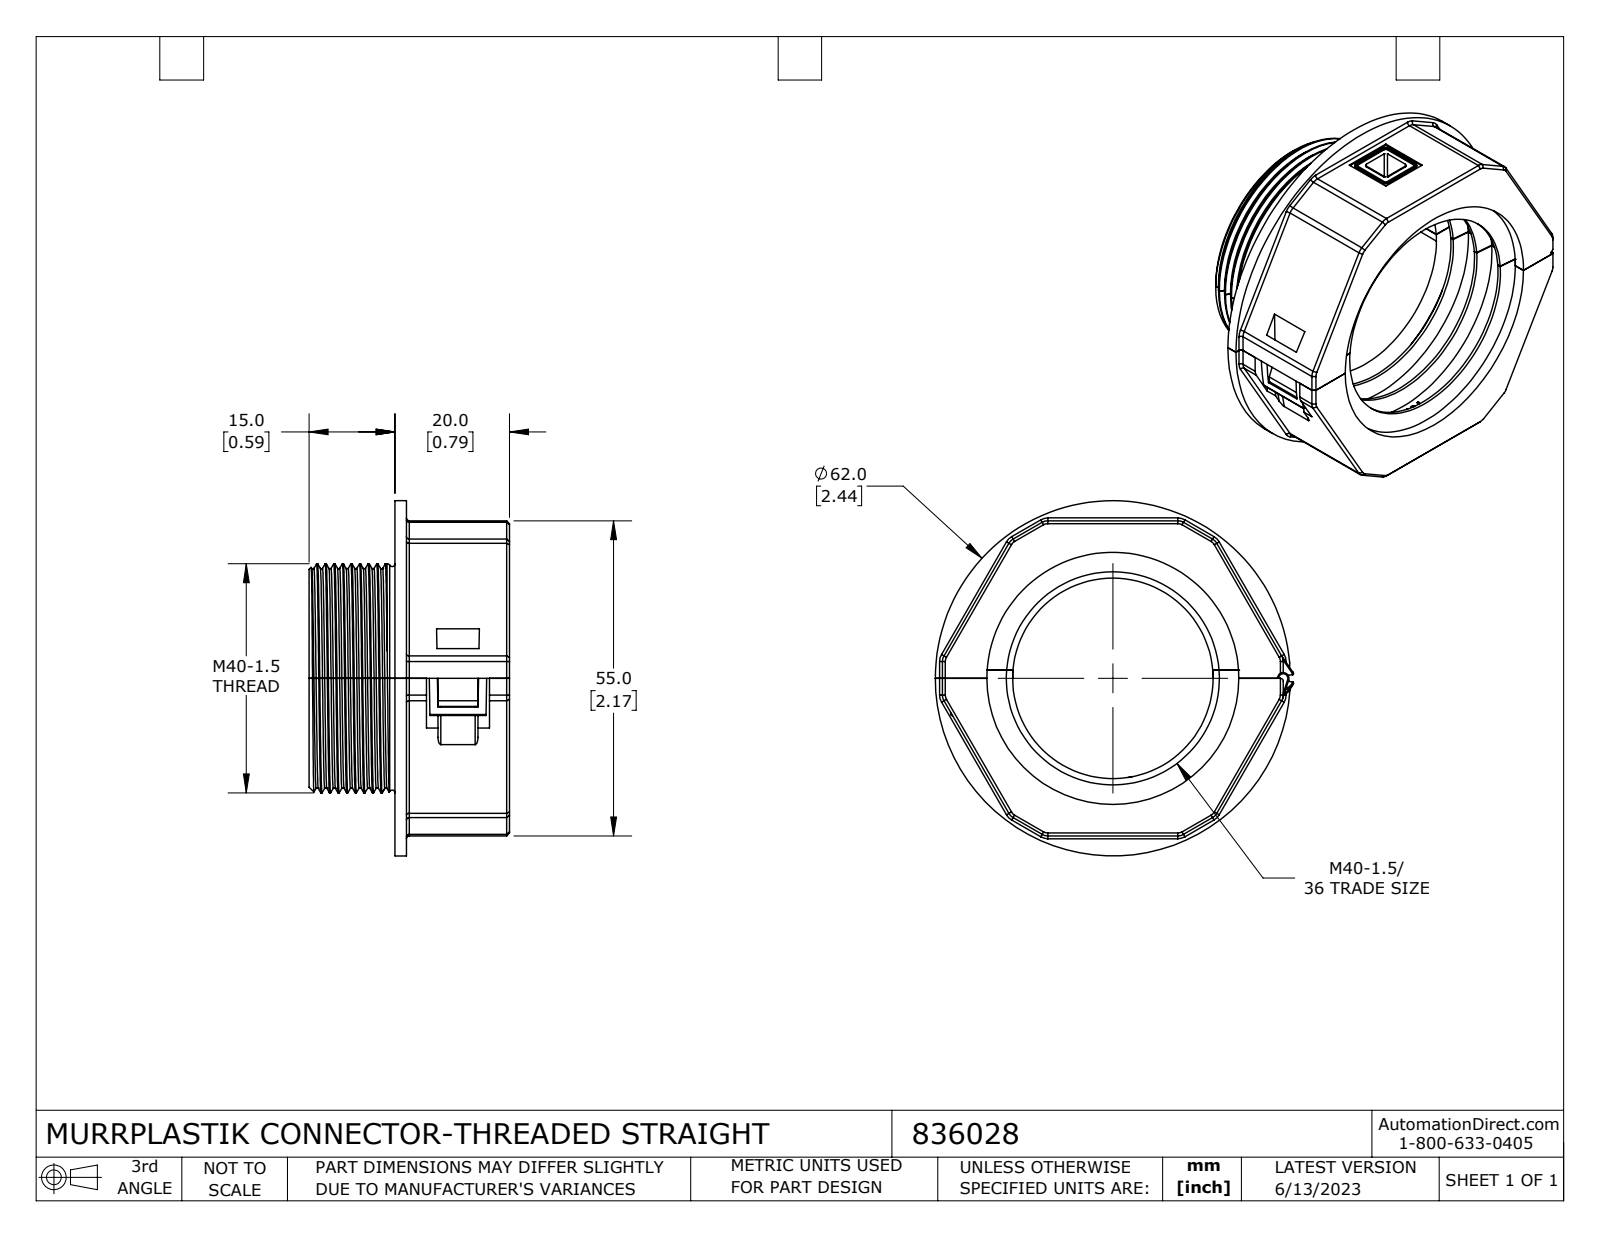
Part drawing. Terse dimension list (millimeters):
name: 836028
written by: SolidWorks 2021 (CONFIG_CONTROL_DESIGN)
unit: mm
bodies: 2 solids, 722 faces (311 planar, 170 cylindrical, 241 other)
size: 62.6 × 62 × 35
volume: 28 170 mm³; area: 18 850 mm²
holes: 1× ⌀2, 1× ⌀5, 1× ⌀35, 1× ⌀37.2, 1× ⌀44
bosses: 1× ⌀62, 1× ⌀40
rounds: 29× R0.2, 21× R0.5, 19× R2, 4× R0.3, 4× R0.4, 4× R0.6, 1× R2.5, 1× R17.7
face distances: 55, 20, 17, 27.5, 3, 18, 1, 2, 59.5, 35
hole spacings: 29.7
